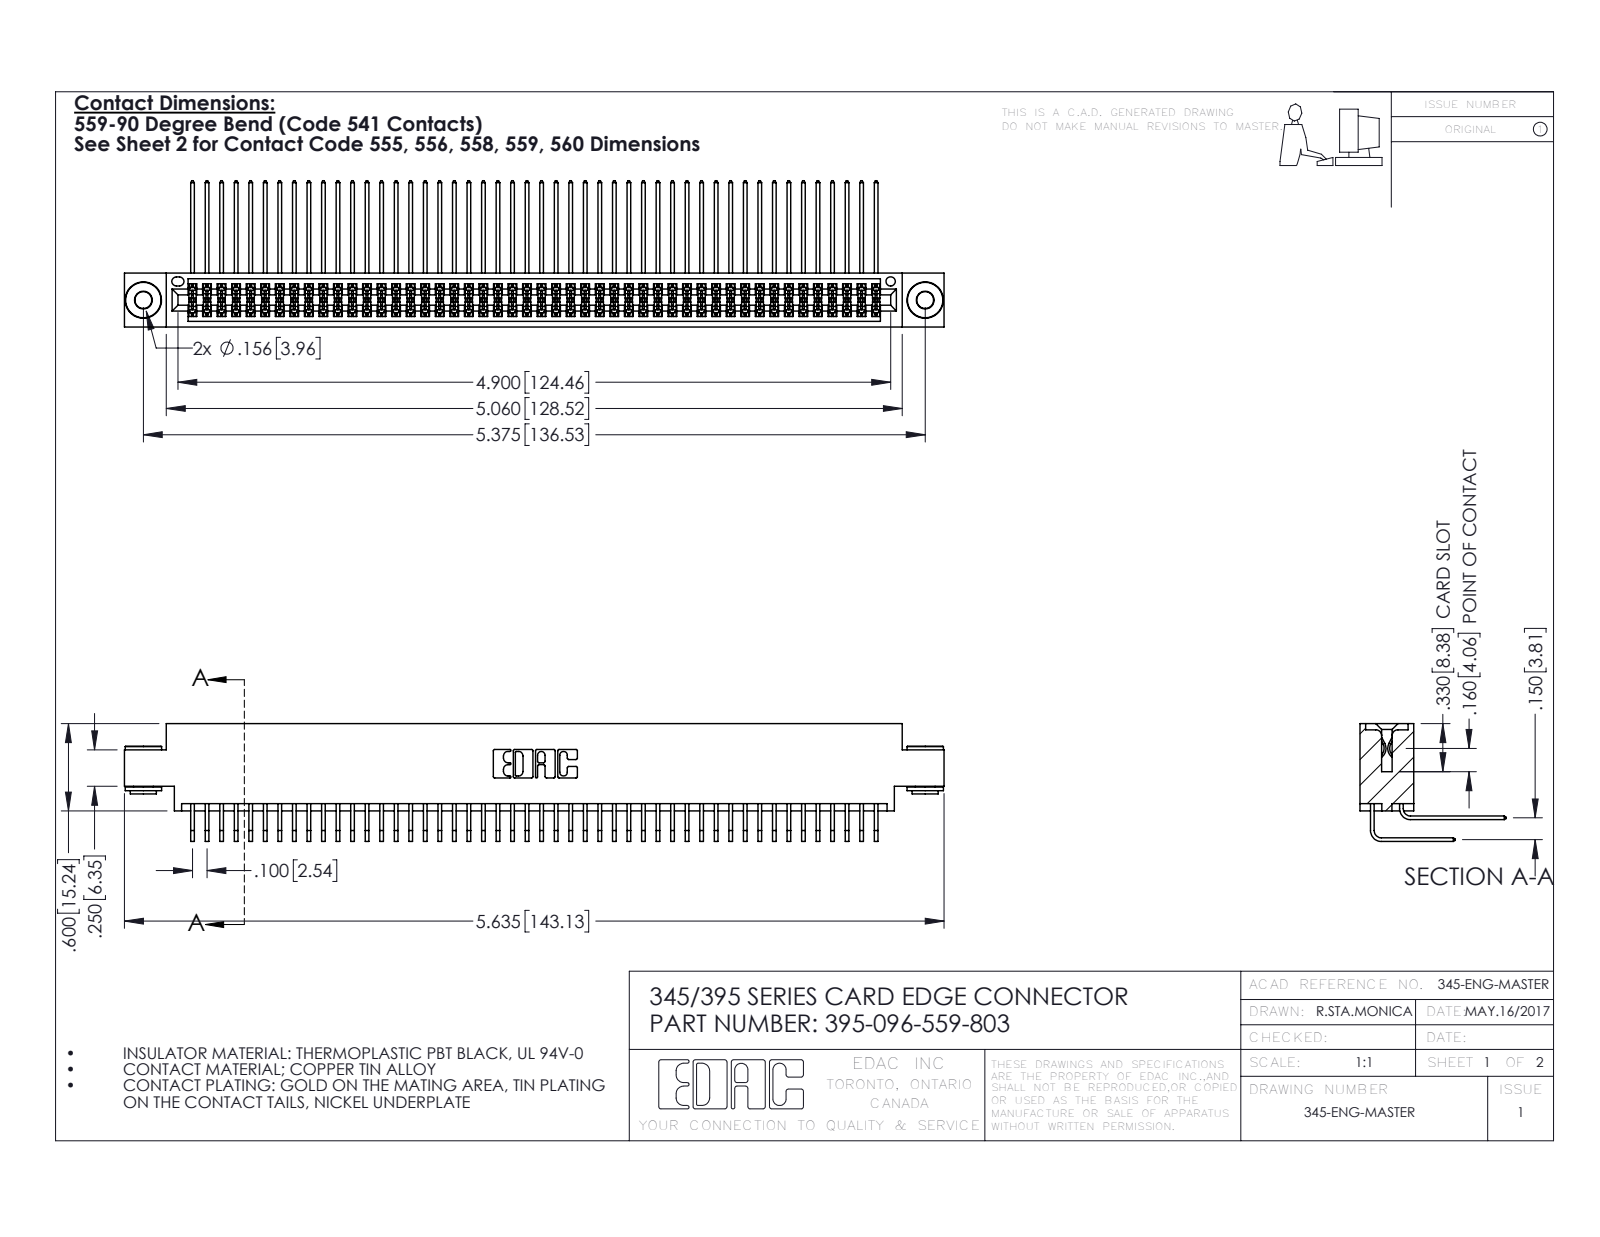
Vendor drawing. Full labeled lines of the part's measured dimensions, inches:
Part name (STEP PRODUCT): 345-292-001_559 Tail - 2; 395-096-559-803; 345-292-001_558 559 Tail - 1; 345-250-002_345-250-002-102 (+1 more)
STEP written by: SolidWorks 2016 (CONFIG_CONTROL_DESIGN)
Units: inches
Bodies: 99 solids, 5160 faces (3454 planar, 1698 cylindrical, 8 other)
Overall size (bounding box): 5.635 × 1.005 × 0.809
Volume: 0.88 in³ · Surface area: 37.79 in²
Round holes (diameter × count): ⌀0.116 ×2, ⌀0.156 ×2, ⌀0.064 ×1
Round bosses / shafts (diameter × count): ⌀0.25 ×2, ⌀0.18 ×2, ⌀0.136 ×2
Partial cylindrical surfaces — rounded edges, fillets, slot ends (radius × count): R0.006 ×145, R0.01 ×22, R0.007 ×6, R0.031 ×6, R0.026 ×3, R0.014 ×2, R0.019 ×2, R0.022 ×2
Main face-to-face distances: 0.072, 0.298, 0.37, 0.2, 0.098, 0.272, 0.025, 0.175, 0.225, 0.15
Hole centre spacings: 0.27, 5.139, 5.375
